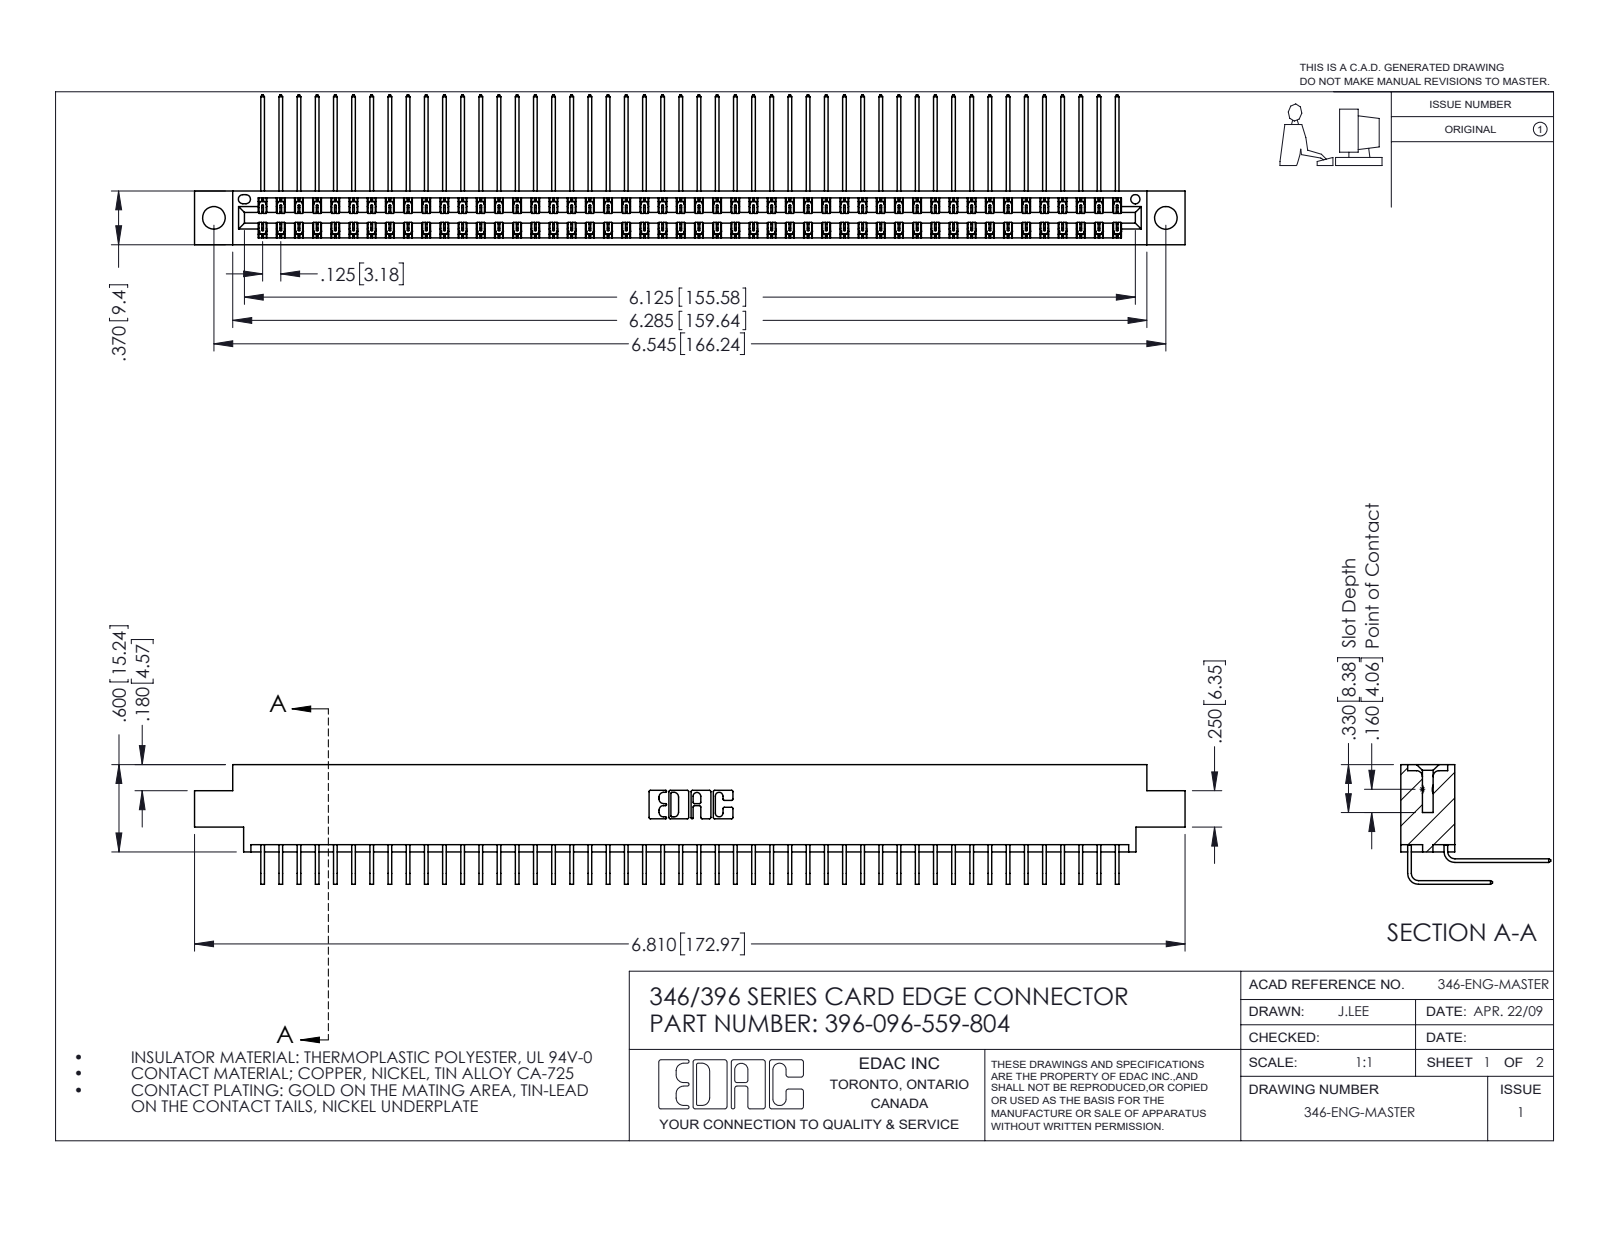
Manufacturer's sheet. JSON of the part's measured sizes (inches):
{"part_name": "346 Part_0.170 Offset - 0.156 Dia-TH; 345-292-001_558 559 Tail - 1; 345-292-001_559 Tail - 2; 396-096-559-804", "step_written_by": "SolidWorks 2016 (CONFIG_CONTROL_DESIGN)", "units": "inches", "bodies": {"solids": 97, "faces": 5310, "planar": 3632, "cylindrical": 1678, "other": 0}, "overall_size": [6.81, 1.03, 0.823], "volume_in3": 1.051, "surface_area_in2": 40.95, "round_holes": [[0.156, 2], [0.064, 1]], "partial_cylinders_radius": [[0.006, 144], [0.01, 22], [0.007, 6], [0.031, 6], [0.026, 3], [0.014, 2], [0.022, 2], [0.024, 2]], "face_to_face_distances": [0.048, 0.322, 0.025, 0.37, 0.25, 0.072, 0.298, 0.275, 0.148, 0.222], "hole_center_spacings": [0.246, 6.336, 6.545]}
